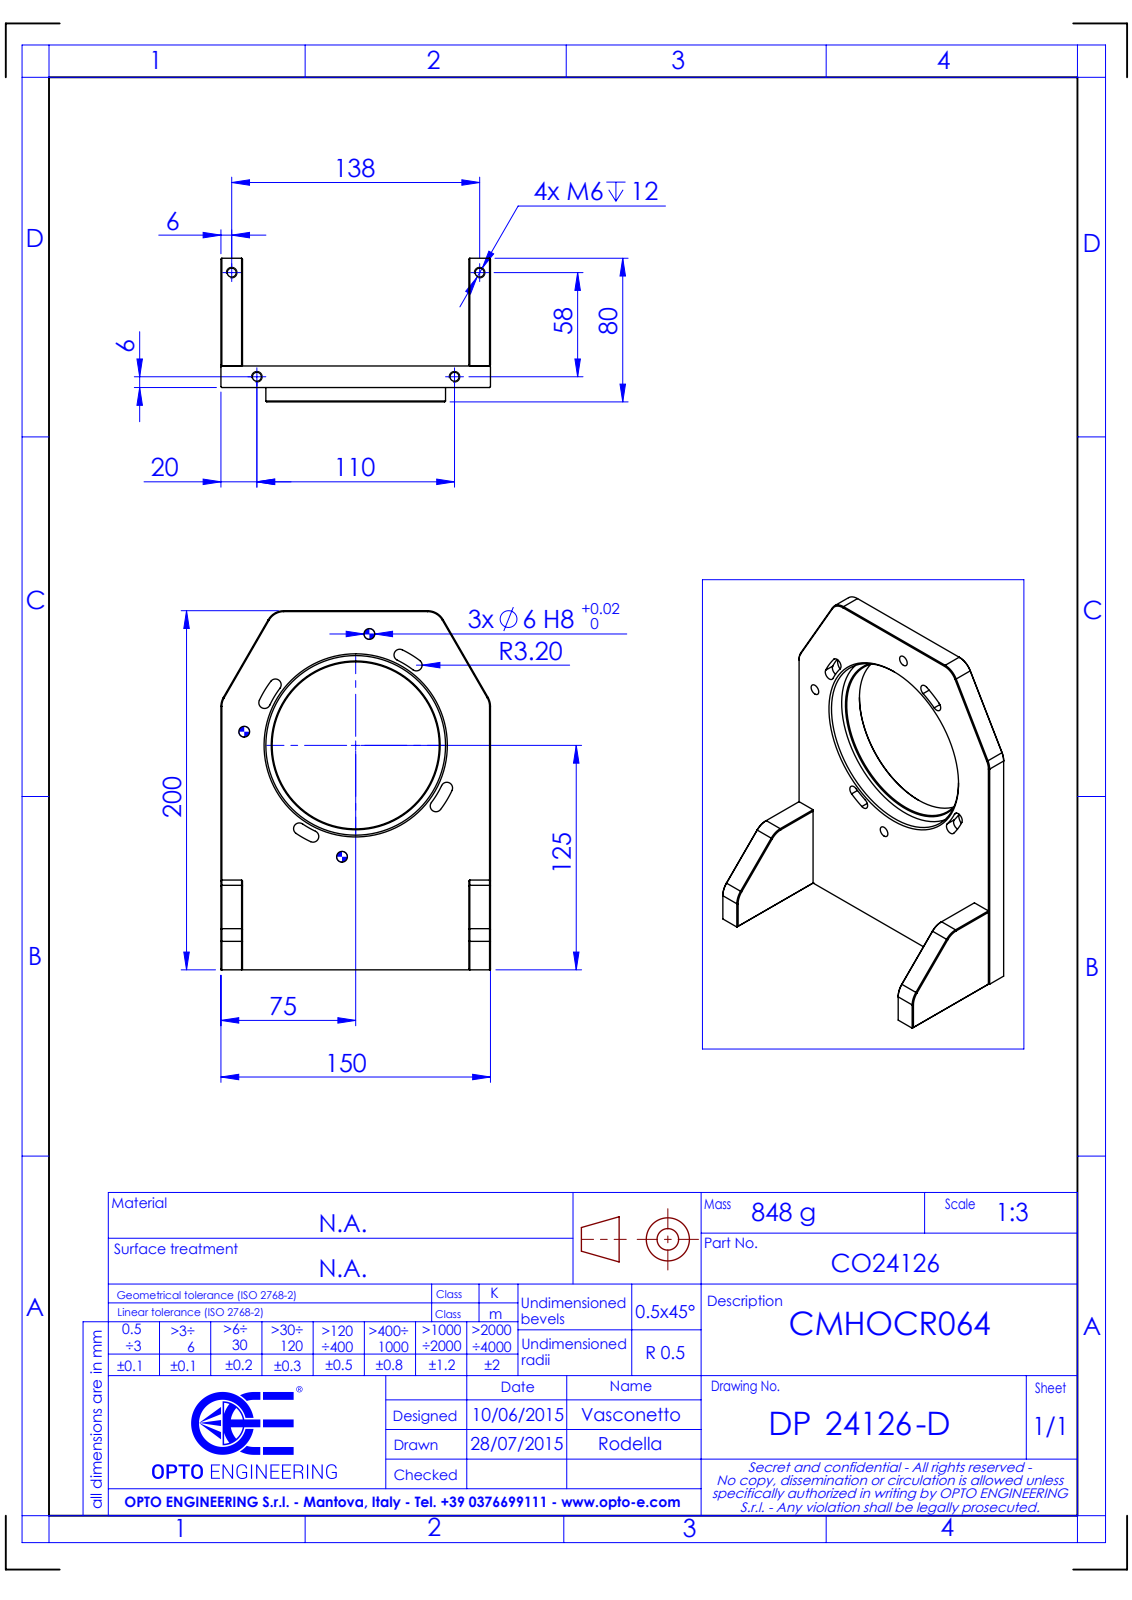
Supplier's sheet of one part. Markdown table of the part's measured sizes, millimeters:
| quantity | value |
| --- | --- |
| part name | DP24126-D_CMHOCR064 |
| STEP written by | SolidWorks 2021 (CONFIG_CONTROL_DESIGN) |
| units | millimeters |
| bodies | 0 solids, 202 faces (82 planar, 80 cylindrical, 40 other) |
| overall size | 200 × 150 × 80 |
| round holes (diameter × count) | 5 × 4, 11 × 4, 6 × 3, 93 × 1, 100 × 1 |
| round bosses / shafts (diameter × count) | 10 × 2 |
| partial cylindrical surfaces (radius × count) | 3.2 × 8, 5.5 × 8, 10 × 6, 50.5 × 1, 52.8 × 1, 59.2 × 1, 61.5 × 1 |
| main face-to-face distances | 12, 138, 150, 126, 3, 9, 200, 8, 11, 20 |
| hole center spacings | 62.5, 138, 30, 59.67, 88.38, 109.48, 134.11, 136.89 |
